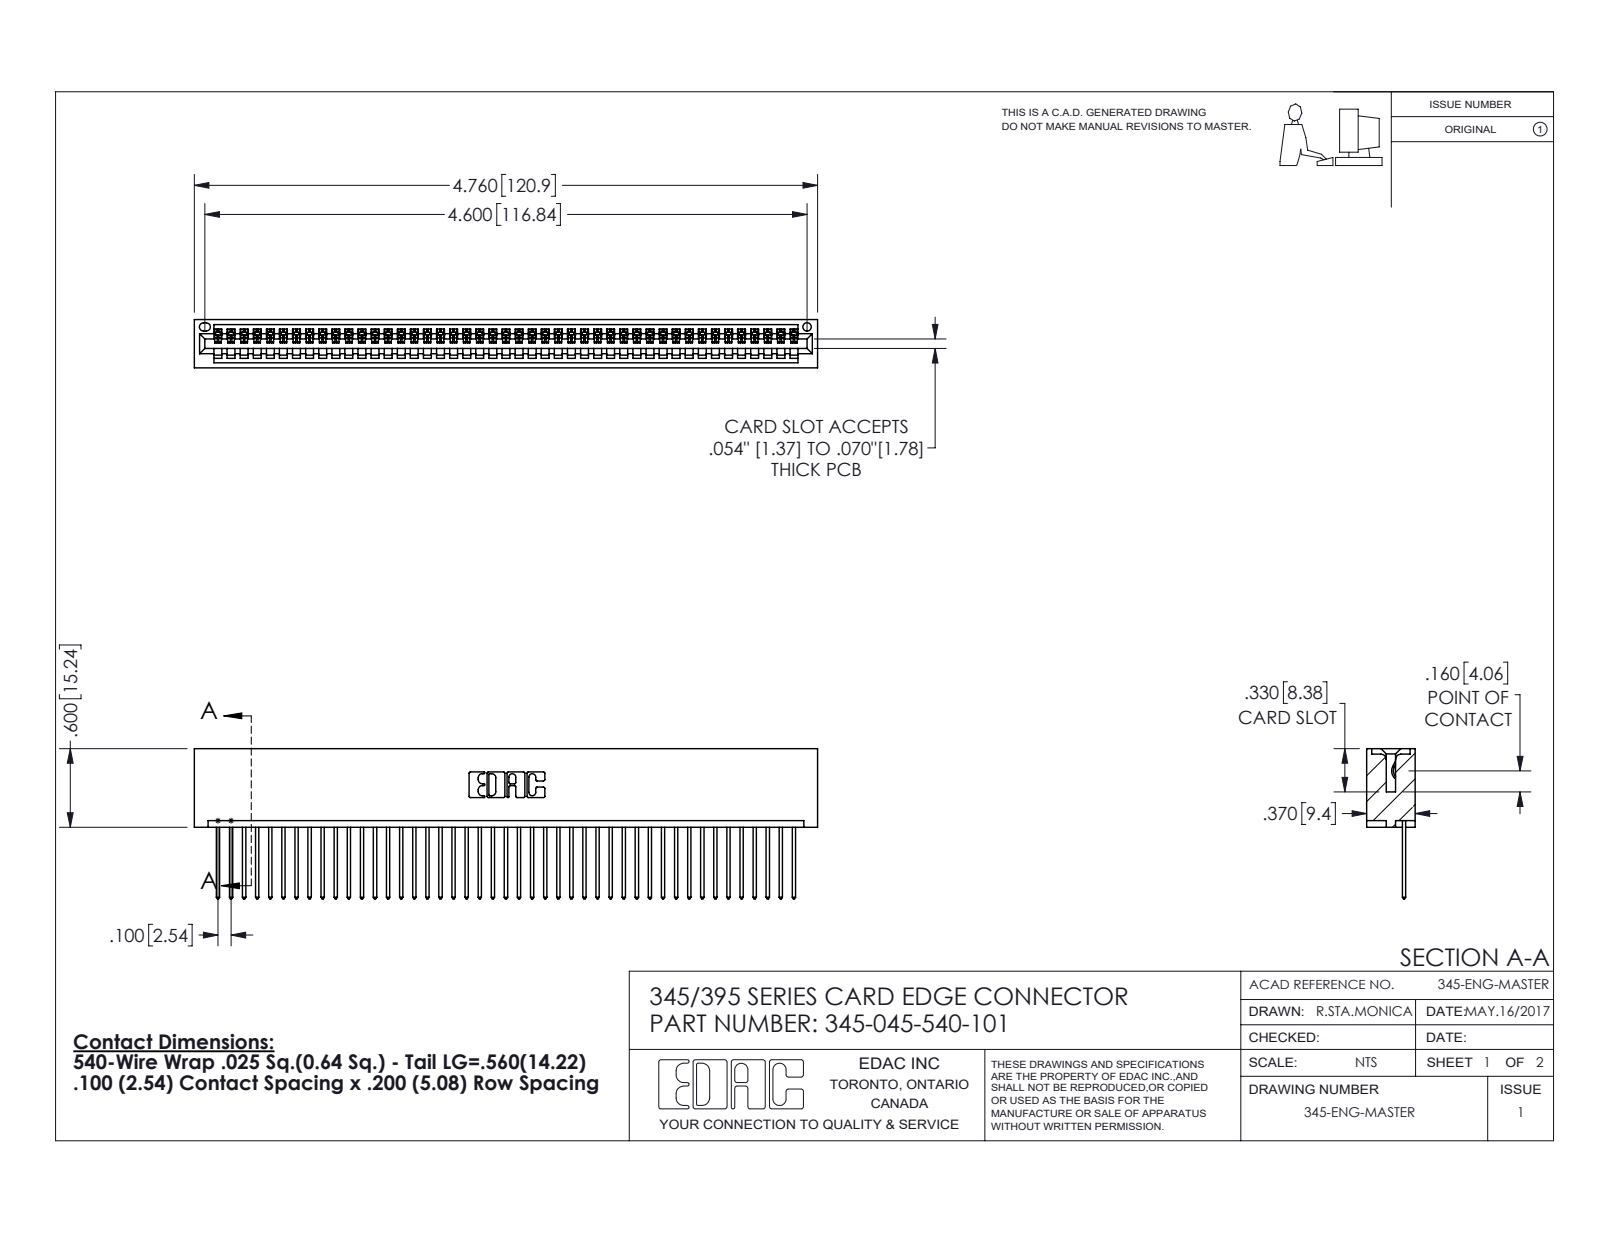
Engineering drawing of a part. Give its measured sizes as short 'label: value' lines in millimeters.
name: 345-292-001_345-293-140; 345-045-540-101; 345 Part_No Mounting Lugs
written by: SolidWorks 2016 (CONFIG_CONTROL_DESIGN)
unit: mm
bodies: 46 solids, 2728 faces (1876 planar, 852 cylindrical, 0 other)
size: 120.9 × 29.1 × 9.4
volume: 12 200 mm³; area: 16 820 mm²
holes: 1× ⌀1.6
rounds: 90× R0.2, 90× R0.3, 22× R0.3, 6× R0.2, 6× R0.8, 3× R0.7, 2× R0.8, 2× R1
face distances: 1.8, 7.6, 2.5, 6.9, 0.6, 9.4, 5.1, 5.7, 3.8, 1.8
